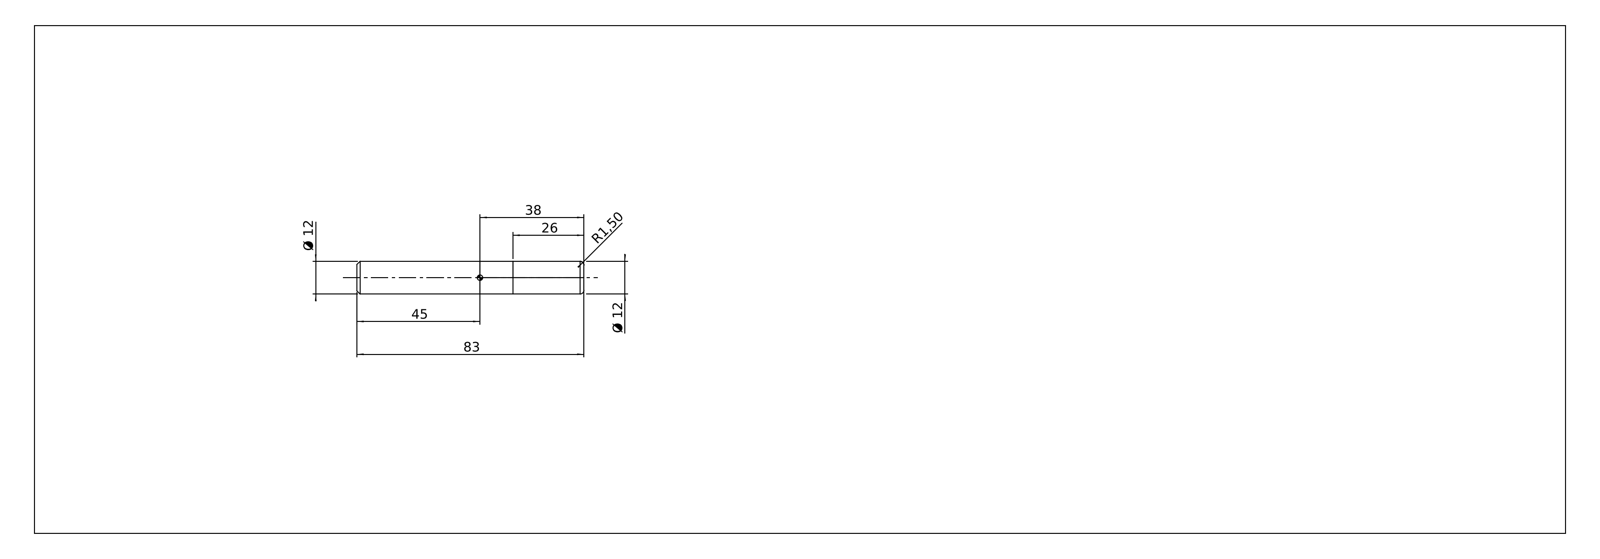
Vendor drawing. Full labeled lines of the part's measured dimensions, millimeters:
Part name (STEP PRODUCT): 734.122.00
STEP written by: SolidWorks 2019 (CONFIG_CONTROL_DESIGN)
Units: millimetres
Bodies: 2 solids, 8 faces (4 planar, 2 cylindrical, 2 other)
Overall size (bounding box): 83 × 12 × 12
Volume: 9 345 mm³ · Surface area: 3 528 mm²
Round bosses / shafts (diameter × count): ⌀12 ×1
Main face-to-face distances: 57, 26, 83
